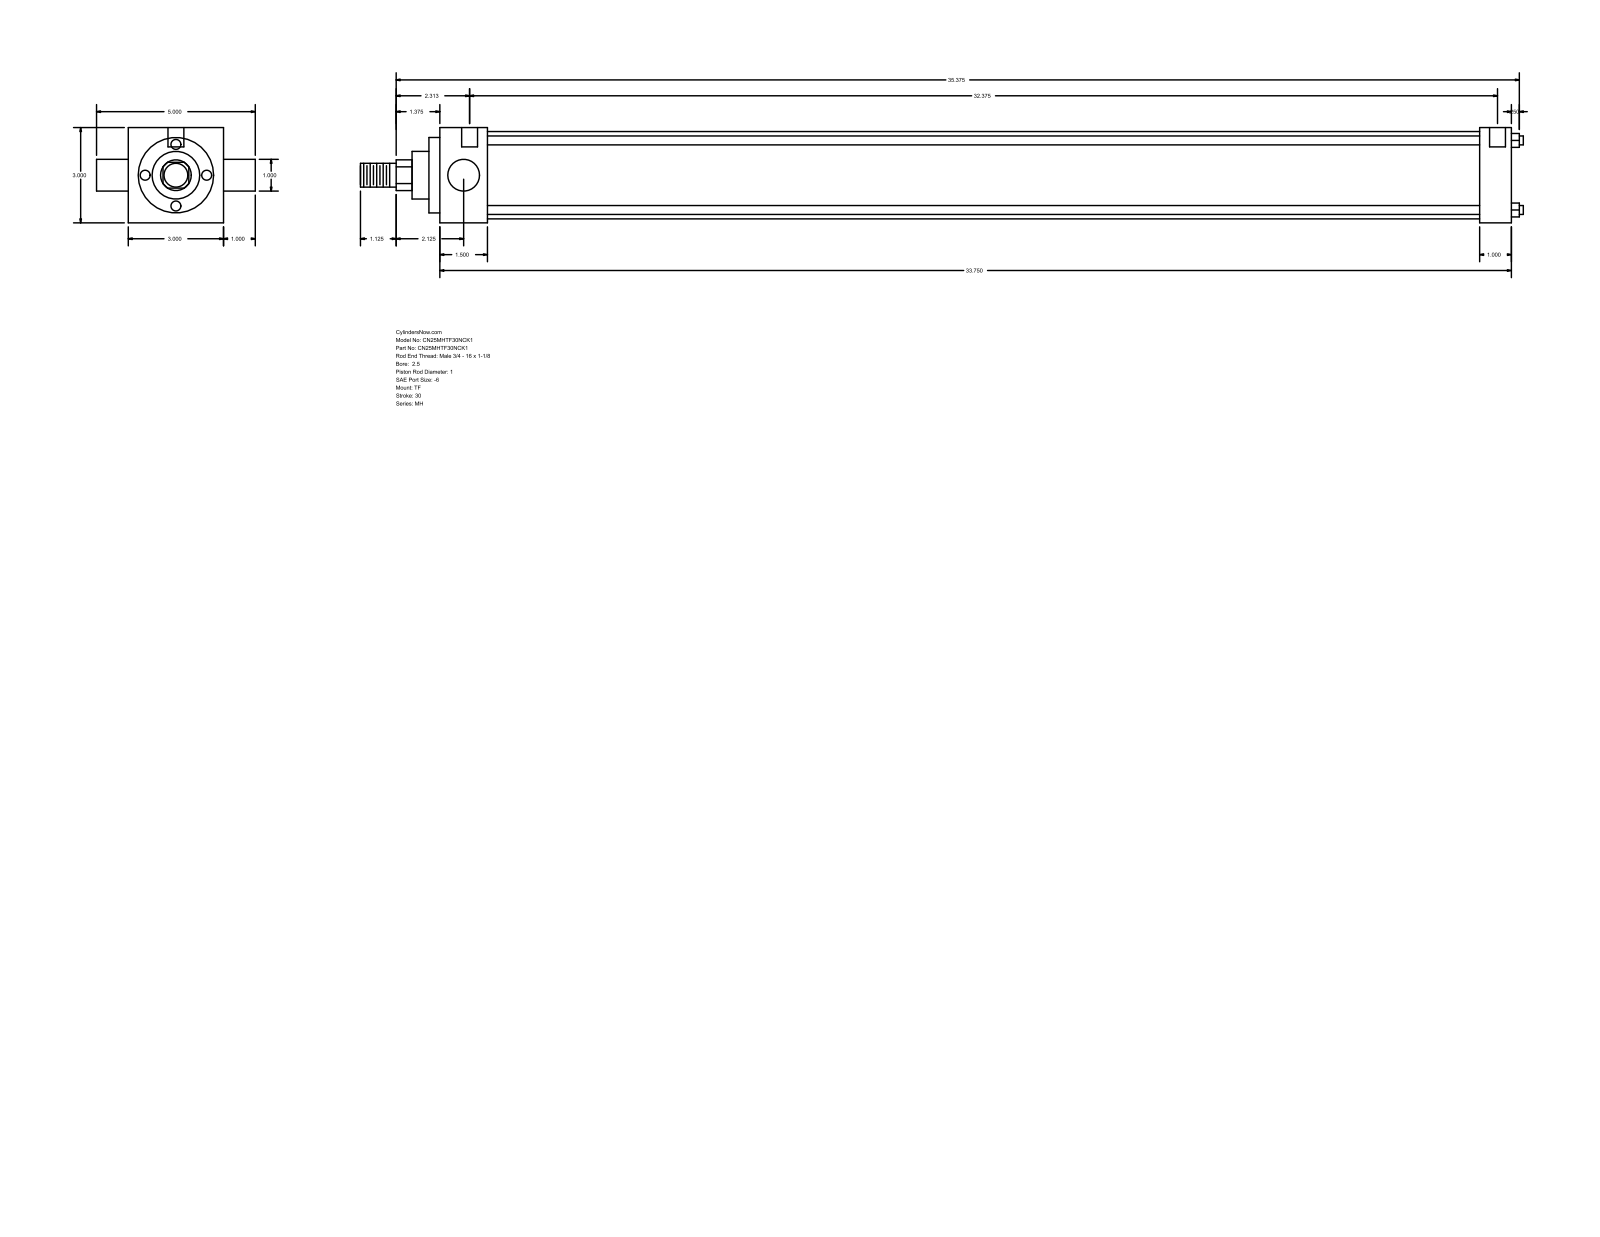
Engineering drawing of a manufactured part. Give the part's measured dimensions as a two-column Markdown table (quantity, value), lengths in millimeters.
| quantity | value |
| --- | --- |
| part name | MH_TF__0250_1 |
| STEP written by | GSSL Pune (CONFIG_CONTROL_DESIGN) |
| units | millimeters |
| bodies | 0 solids, 86 faces (61 planar, 25 cylindrical, 0 other) |
| overall size | 930.27 × 127 × 76.2 |
| round holes (diameter × count) | 5.56 × 3, 12.7 × 2 |
| round bosses / shafts (diameter × count) | 7.14 × 4, 25.4 × 2, 69.85 × 1, 60.33 × 1, 38.1 × 1, 19.05 × 1 |
| partial cylindrical surfaces (radius × count) | 12.29 × 1 |
| main face-to-face distances | 76.2, 857.25, 25.4, 38.11, 819.14, 831.85, 793.74, 8.73, 46.84, 840.58 |
| hole center spacings | 3.18, 4.76, 822.32, 825.5, 827.08, 830.26 |
